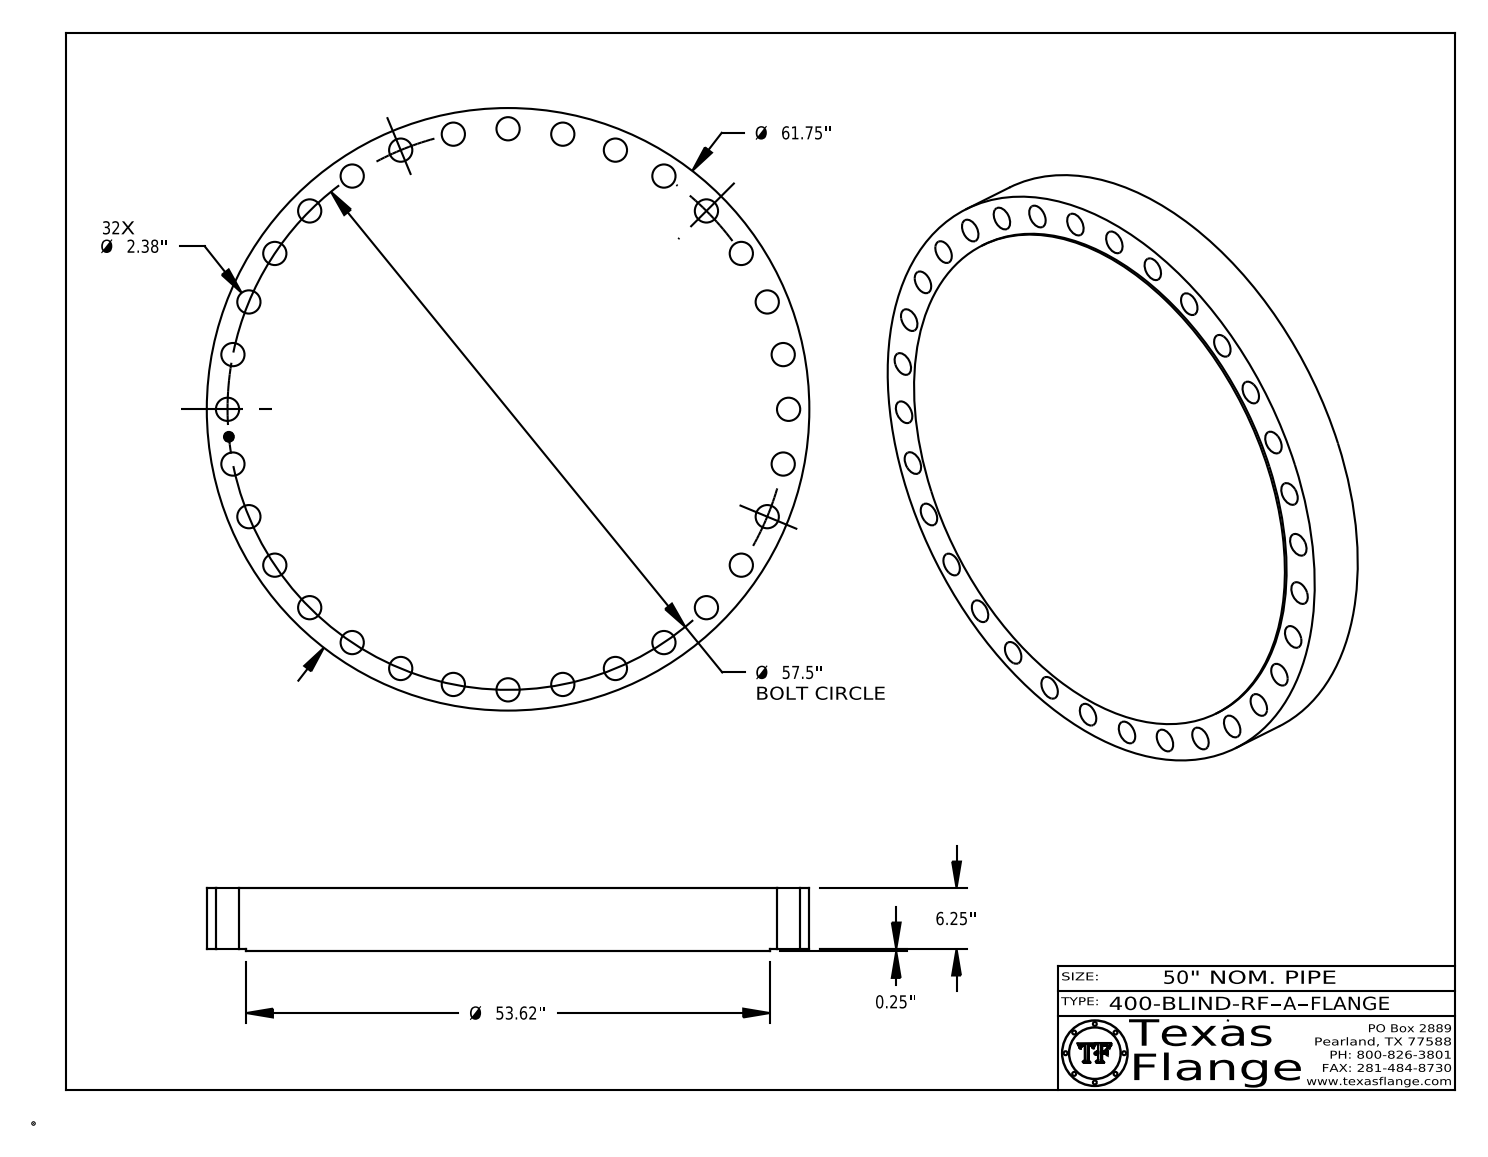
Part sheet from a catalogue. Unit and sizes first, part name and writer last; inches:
Units: inches
Overall size (bounding box): 61.75 × 61.75 × 6.5
Round holes (diameter × count): ⌀2.38 ×32, ⌀1 ×1
Round bosses / shafts (diameter × count): ⌀0.061 ×8, ⌀61.75 ×1, ⌀53.62 ×1, ⌀0.788 ×1
Main face-to-face distances: 6.5, 0.25, 6.25, 0.015, 6.485, 6.235, 0.298, 0.292, 0.054, 0.193
Hole centre spacings: 44.448, 22.004, 57.223, 50.71, 27.105, 55.024, 40.659, 5.636
Volume: 18 392 in³ · Surface area: 8 455 in²
Bodies: 1 solid, 456 faces (368 planar, 88 cylindrical, 0 other)
Part name (STEP PRODUCT): 400-BLIND-RF, Series A
STEP written by: CATIA V5 STEP AP214 (AUTOMOTIVE_DESIGN)
